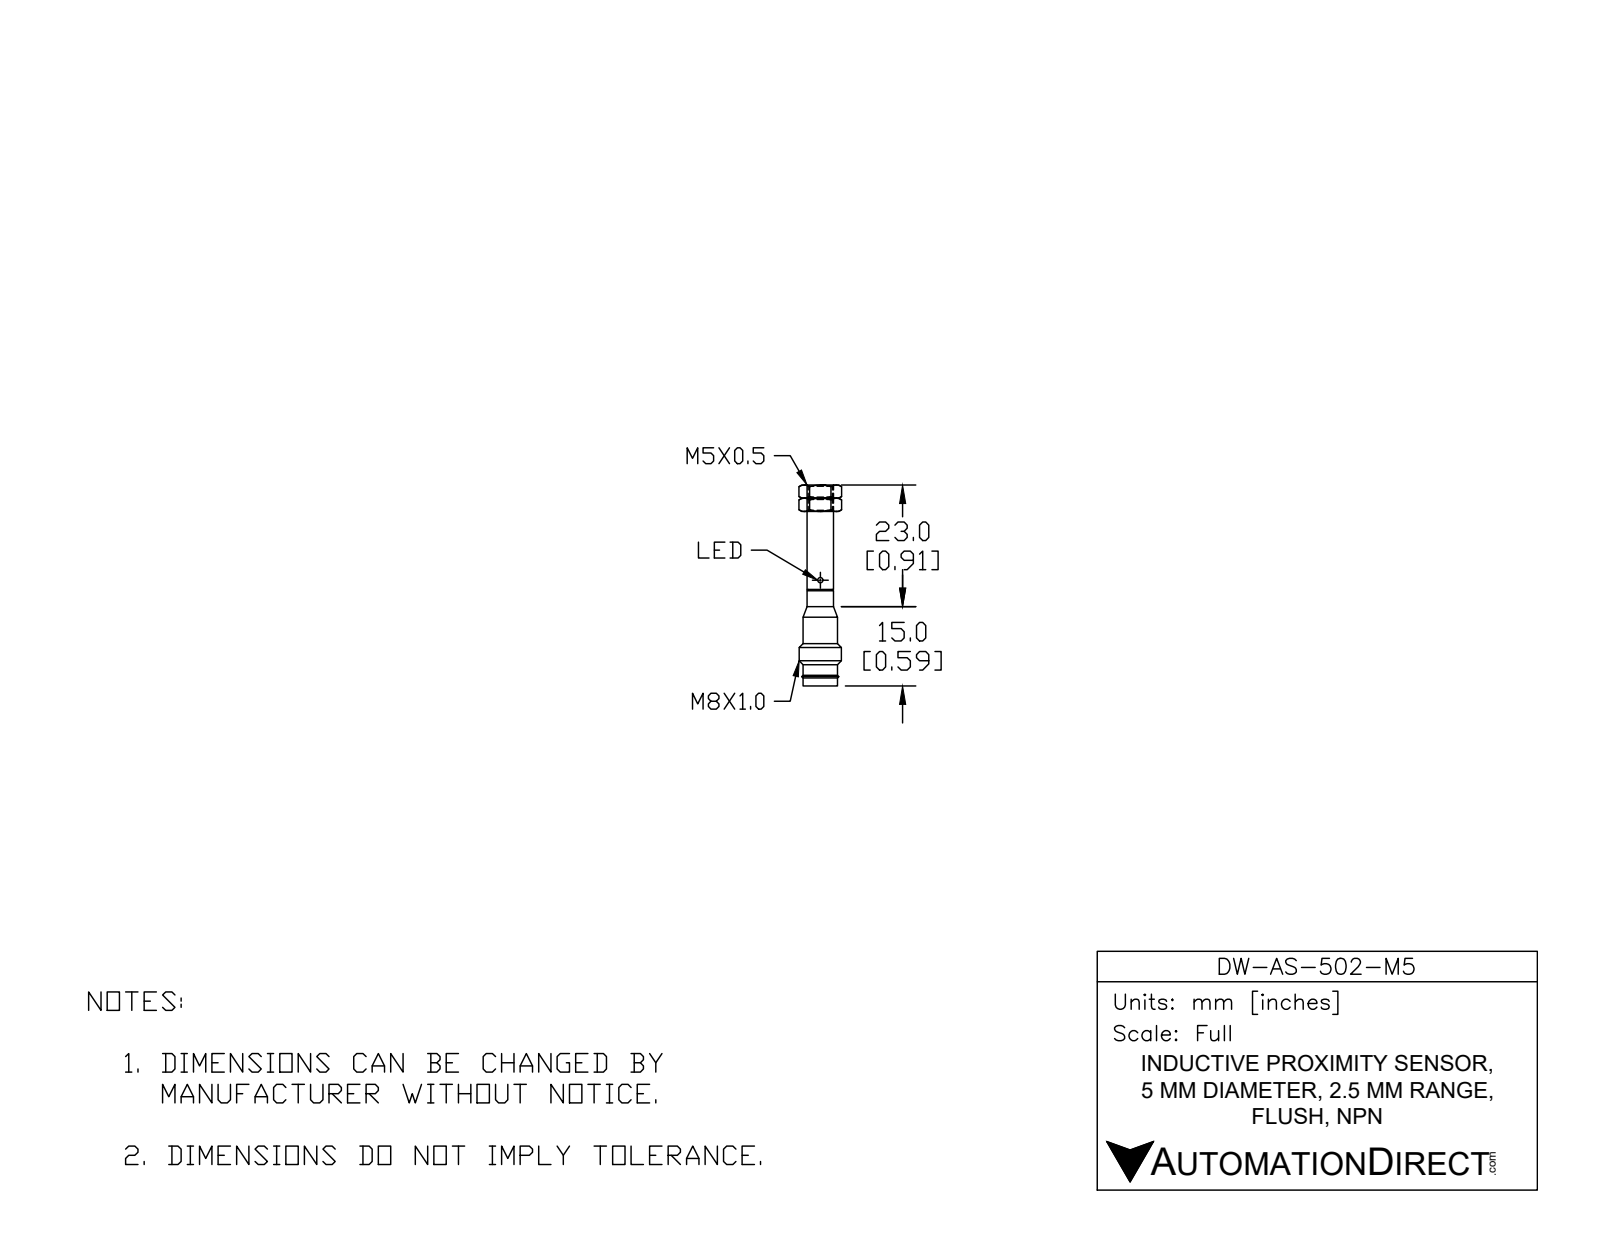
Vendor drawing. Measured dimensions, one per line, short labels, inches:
name: DW-AS-502-M5
written by: SolidWorks 2017 (AUTOMOTIVE_DESIGN)
unit: in
bodies: 4 solids, 42 faces (11 planar, 15 cylindrical, 16 other)
size: 1.496 × 0.315 × 0.315
volume: 0.026 in³; area: 2.173 in²
holes: 1× ⌀0.059, 1× ⌀0.14, 1× ⌀0.217, 1× ⌀0.228
bosses: 3× ⌀0.039, 1× ⌀0.315, 1× ⌀0.272, 1× ⌀0.256, 1× ⌀0.228, 1× ⌀0.197, 1× ⌀0.132
face distances: 0.03, 1.269, 1.299, 1.267, 1.297, 0.051, 0.049, 1.218, 1.248, 0.047
